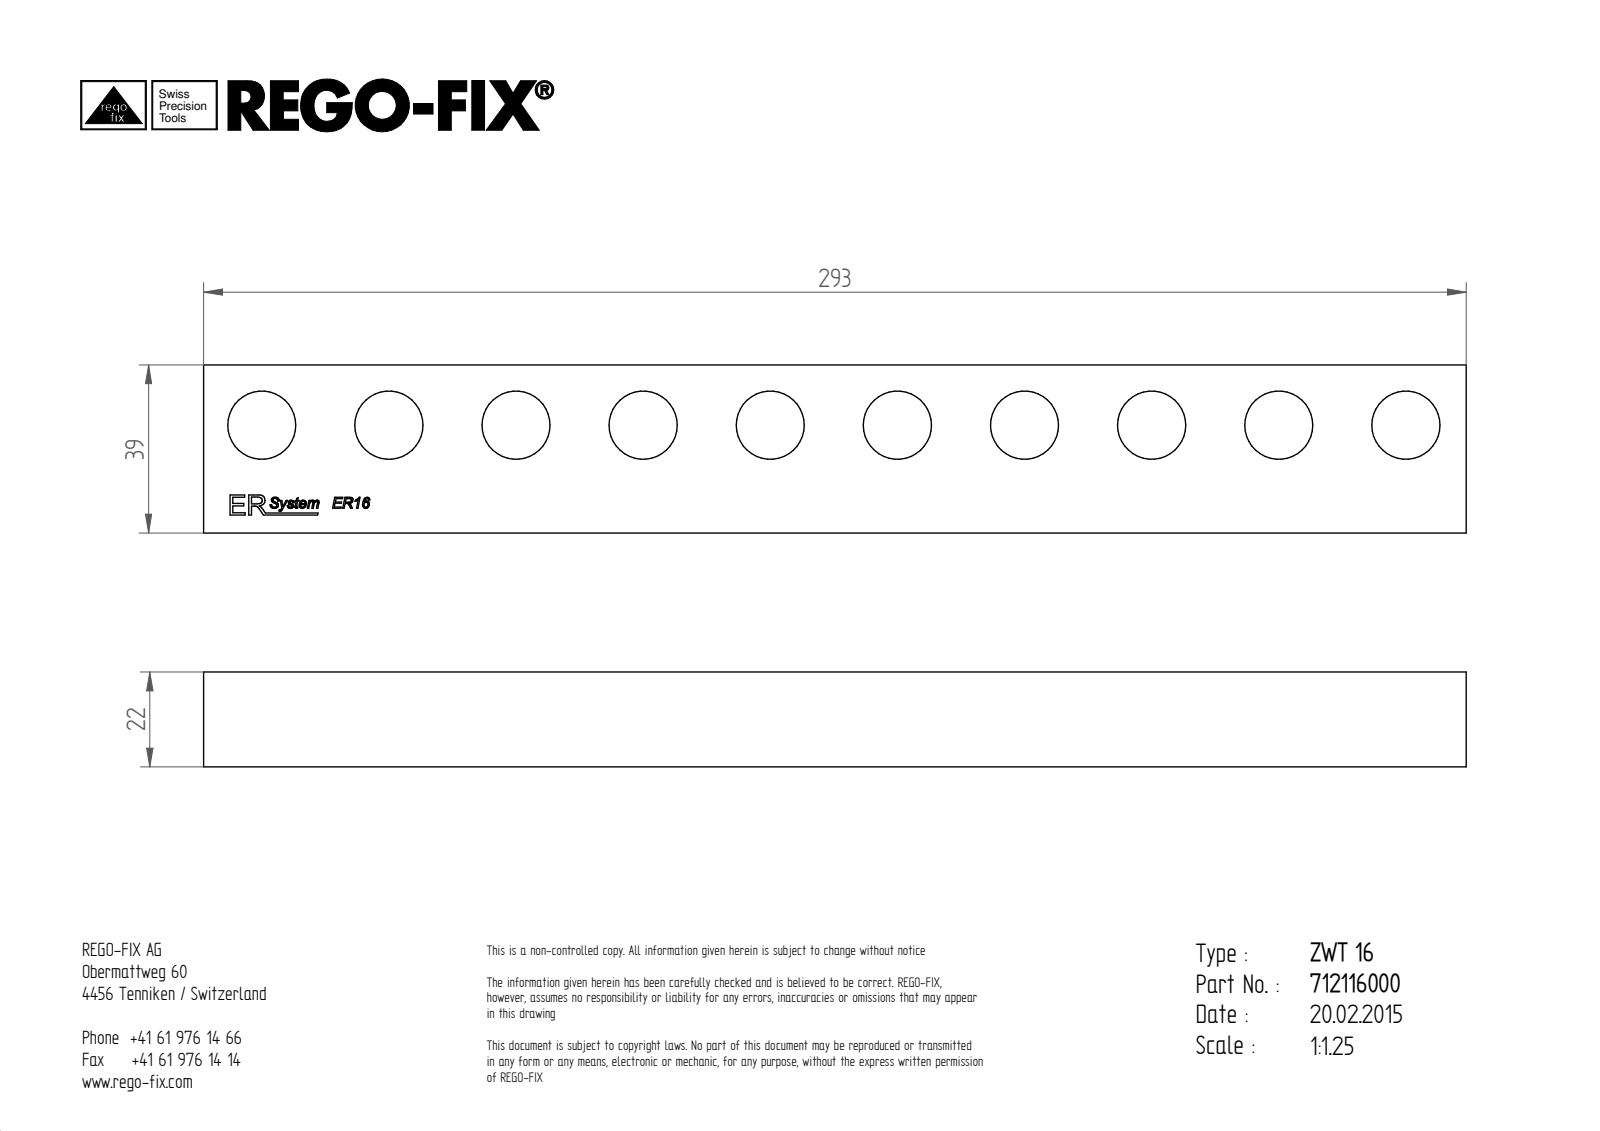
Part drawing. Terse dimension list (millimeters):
written by: Unknown (AUTOMOTIVE_DESIGN)
unit: mm
bodies: 1 solid, 141 faces (102 planar, 10 cylindrical, 29 other)
size: 293 × 39 × 22
volume: 220 020 mm³; area: 45 423 mm²
holes: 10× ⌀15.8
face distances: 22, 39, 6, 16, 293, 21.9, 15.9, 4.13, 34.87, 4.63
hole spacings: 29.5, 59, 88.5, 118, 147.5, 177, 206.5, 236
